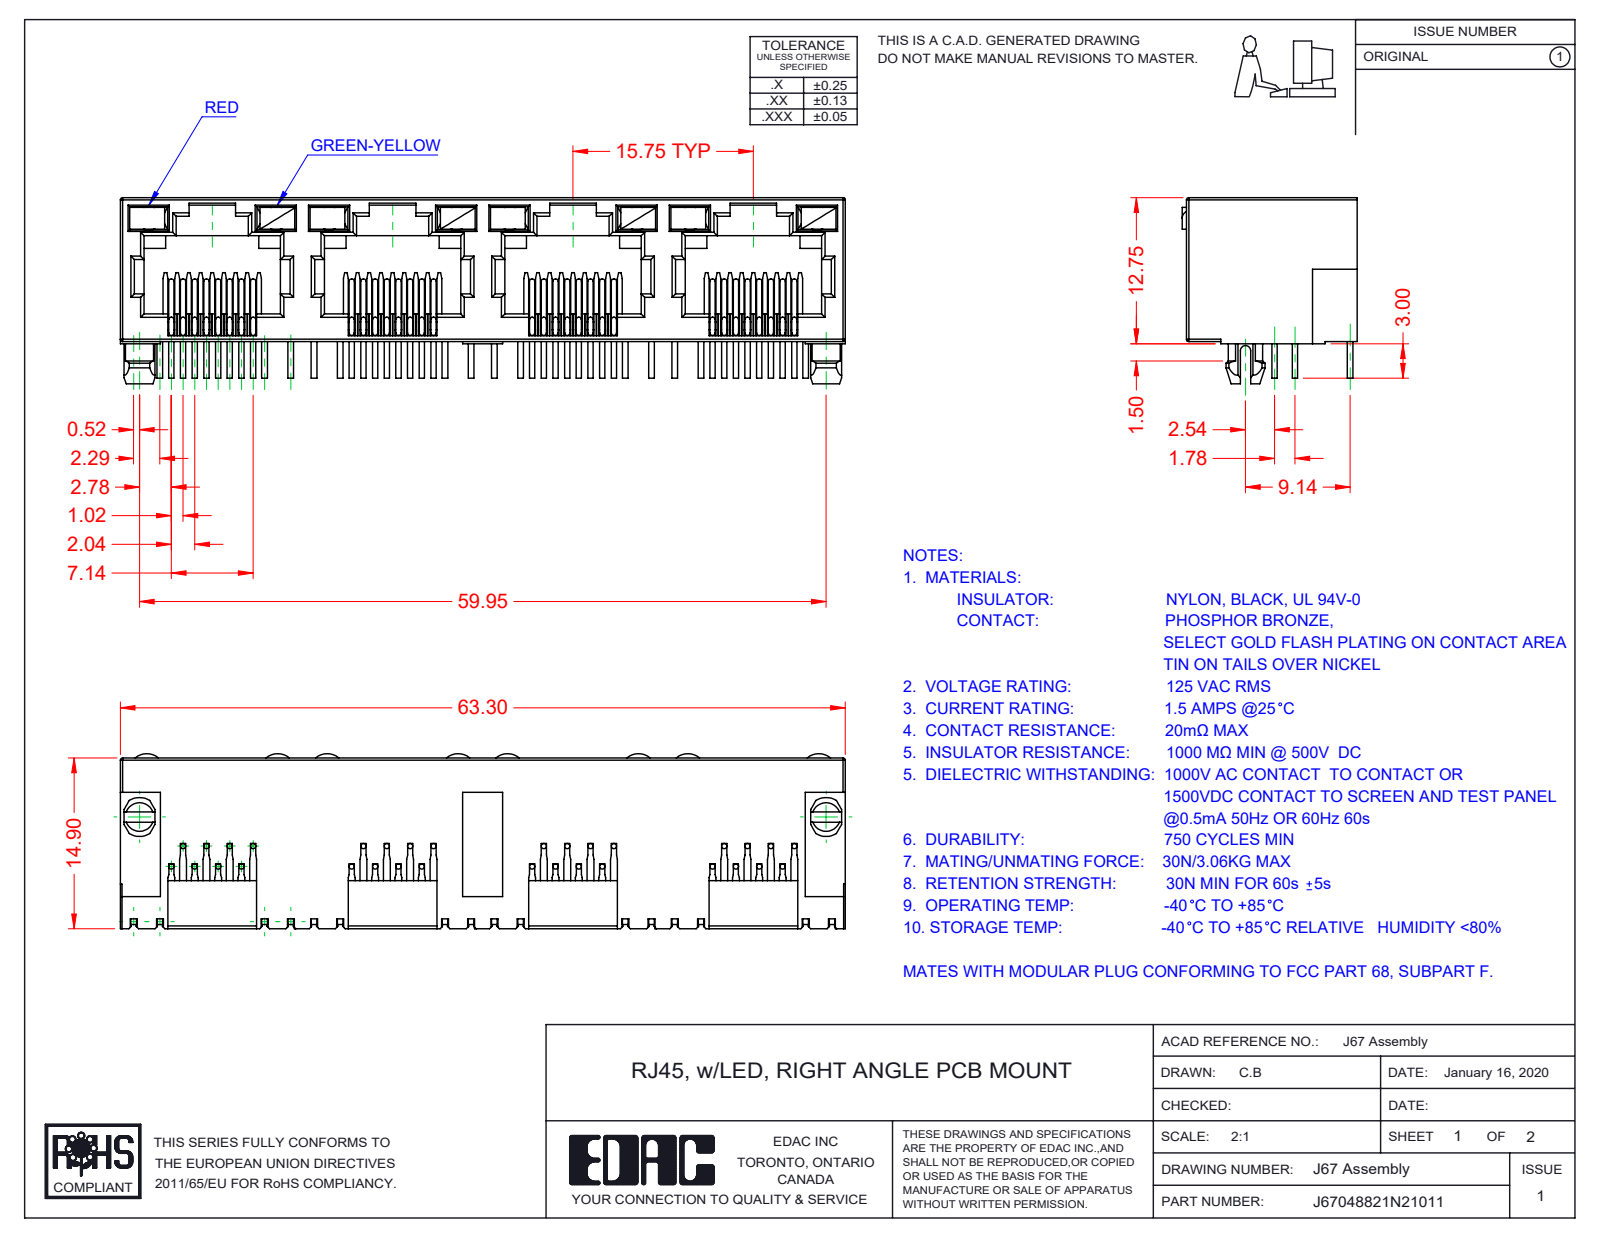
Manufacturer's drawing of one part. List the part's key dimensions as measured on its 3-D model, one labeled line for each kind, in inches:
Part name (STEP PRODUCT): 67 Contacts; 67 Insulator; 67 LED RH_5-Green-Yellow; J67048822N25011 (+1 more)
STEP written by: SolidWorks 2016 (CONFIG_CONTROL_DESIGN)
Units: inches
Bodies: 41 solids, 2473 faces (1781 planar, 484 cylindrical, 208 other)
Overall size (bounding box): 2.492 × 0.64 × 0.602
Volume: 0.315 in³ · Surface area: 17.94 in²
Round bosses / shafts (diameter × count): ⌀0.018 ×96
Partial cylindrical surfaces — rounded edges, fillets, slot ends (radius × count): R0.008 ×66, R0.012 ×29, R0.018 ×9, R0.061 ×8, R0.059 ×2, R0.067 ×2, R0.014 ×1, R0.039 ×1
Main face-to-face distances: 0.02, 0.494, 0.074, 0.035, 0.394, 0.62, 0.039, 0.055, 0.433, 0.468
